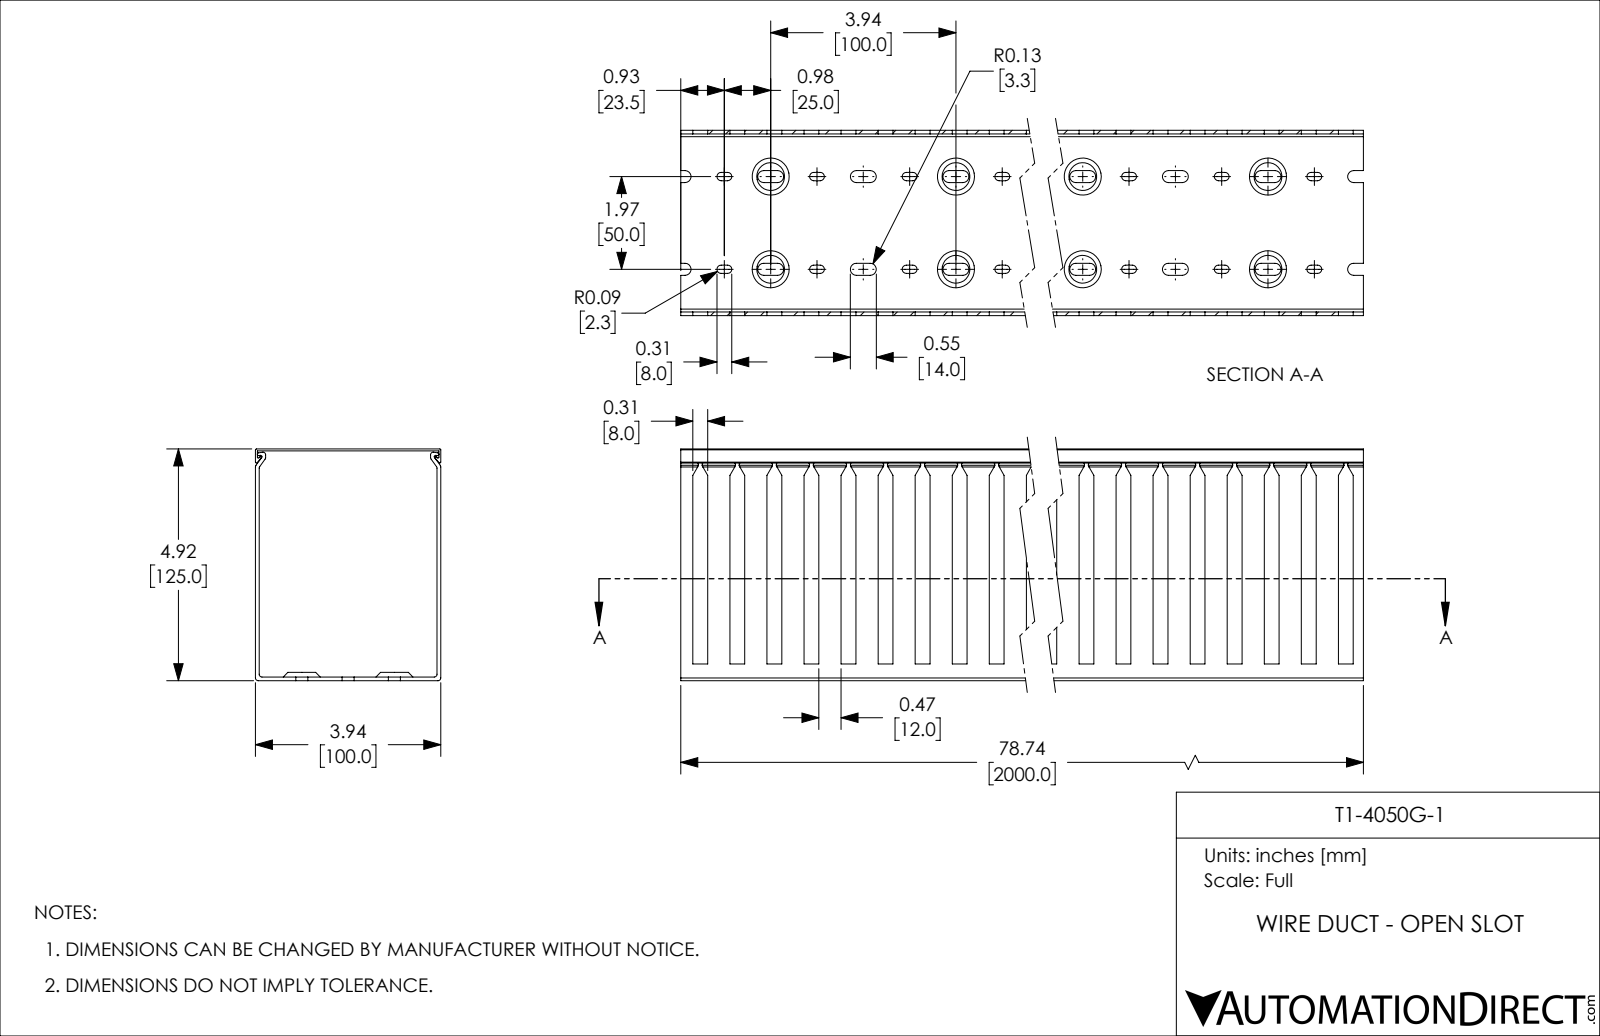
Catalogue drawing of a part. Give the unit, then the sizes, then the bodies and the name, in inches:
Units: inches
Overall size (bounding box): 78.74 × 4.921 × 3.937
Partial cylindrical surfaces — rounded edges, fillets, slot ends (radius × count): R0.128 ×200, R0.089 ×160, R0.059 ×12, R0.02 ×8, R0.03 ×6
Main face-to-face distances: 0.079, 3.858, 3.937, 0.039, 3.78, 4.882, 4.921, 4.803, 4.843, 3.898
Volume: 97.03 in³ · Surface area: 2 841 in²
Bodies: 2 solids, 1573 faces (762 planar, 731 cylindrical, 80 other)
Part name (STEP PRODUCT): T1-4050G-1
STEP written by: SolidWorks 2021 (CONFIG_CONTROL_DESIGN)
